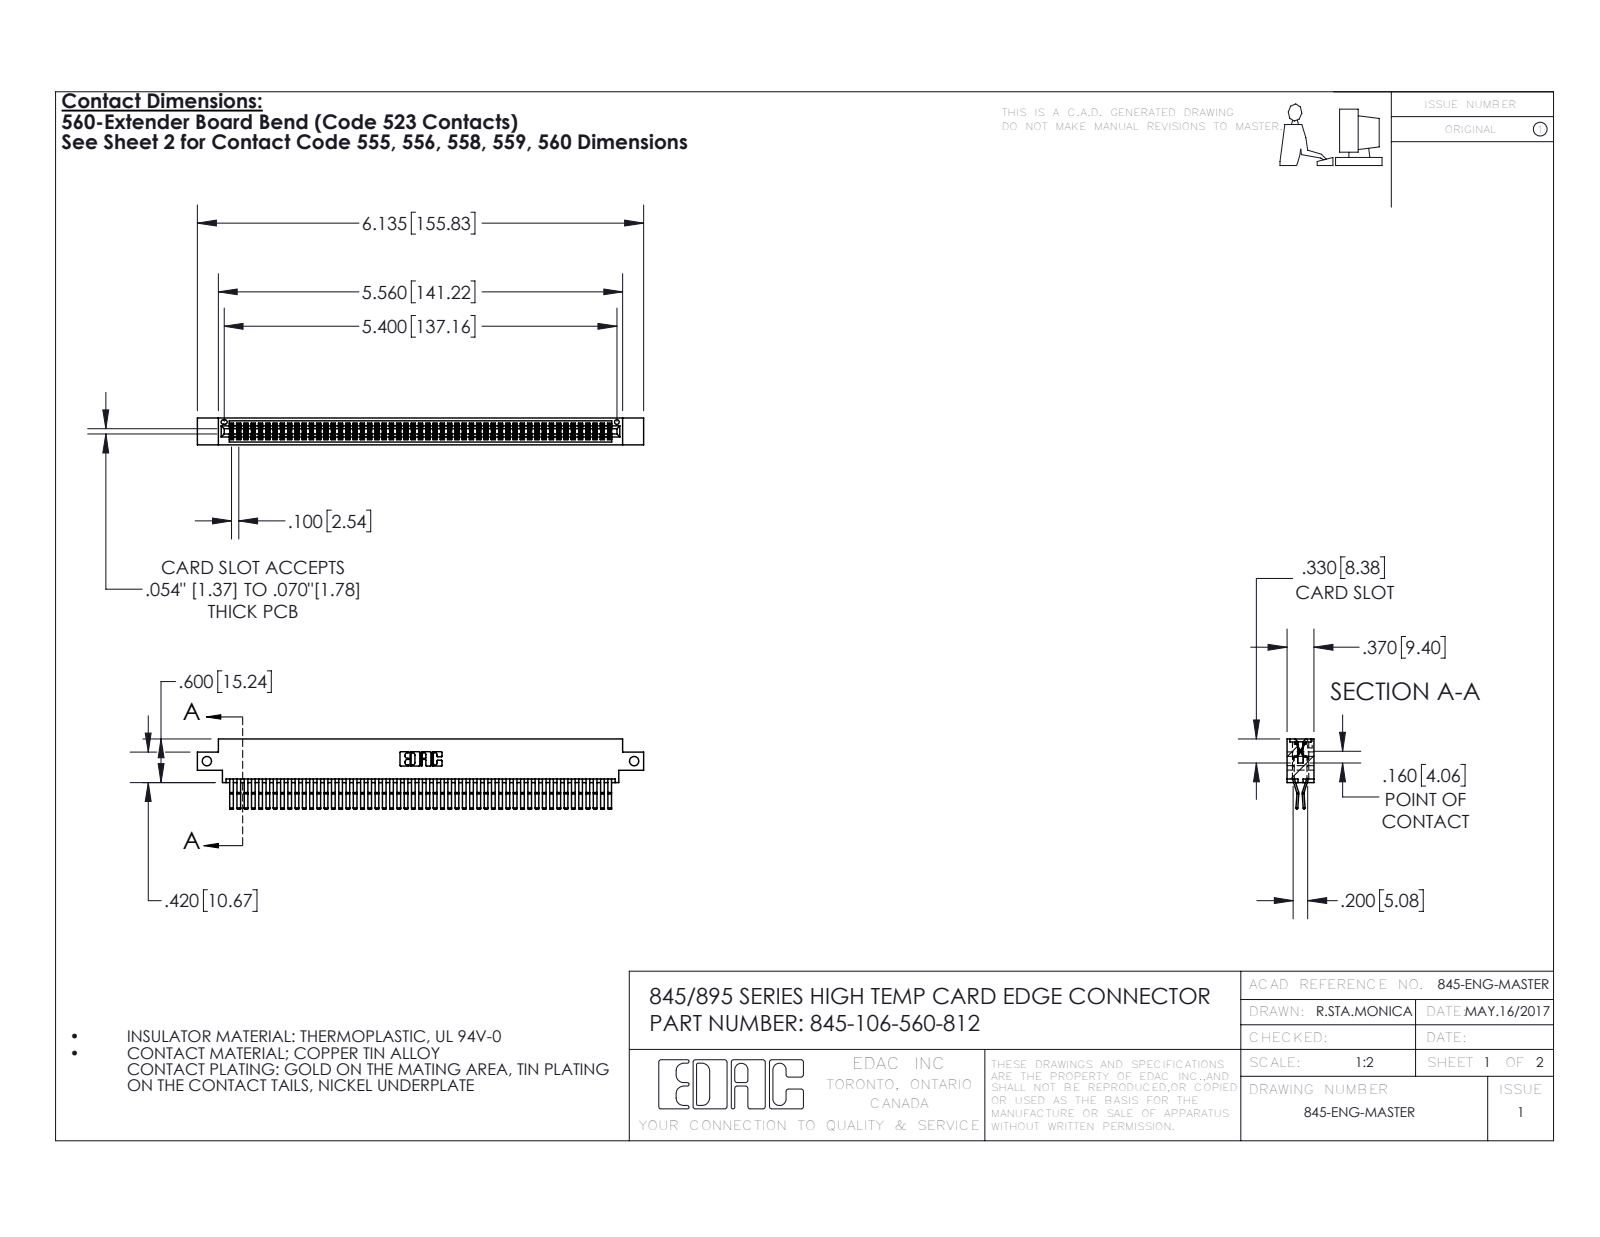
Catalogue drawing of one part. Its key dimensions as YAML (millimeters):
part_name: "345-106-560-812; 345 Part_0.170 Offset - Side Mount; 345-292-001_560 Tail"
step_written_by: "SolidWorks 2016 (CONFIG_CONTROL_DESIGN)"
units: millimeters
bodies: {solids: 107, faces: 5642, planar: 3582, cylindrical: 2060, other: 0}
overall_size: [155.8, 24.4, 9.4]
volume: 15700
surface_area: 25260
round_holes:
  - {diameter: 3.3, count: 2}
  - {diameter: 1.6, count: 1}
partial_cylinders:
  - {radius: 0.2, count: 159}
  - {radius: 0.3, count: 22}
  - {radius: 0.2, count: 6}
  - {radius: 0.8, count: 6}
  - {radius: 0.7, count: 3}
  - {radius: 0.3, count: 2}
  - {radius: 0.4, count: 2}
  - {radius: 0.5, count: 2}
face_to_face_distances: [0.6, 7.6, 1.8, 9.4, 5.1, 2.5, 6.9, 5.7, 4.4, 3.8]
hole_center_spacings: [149.2]
